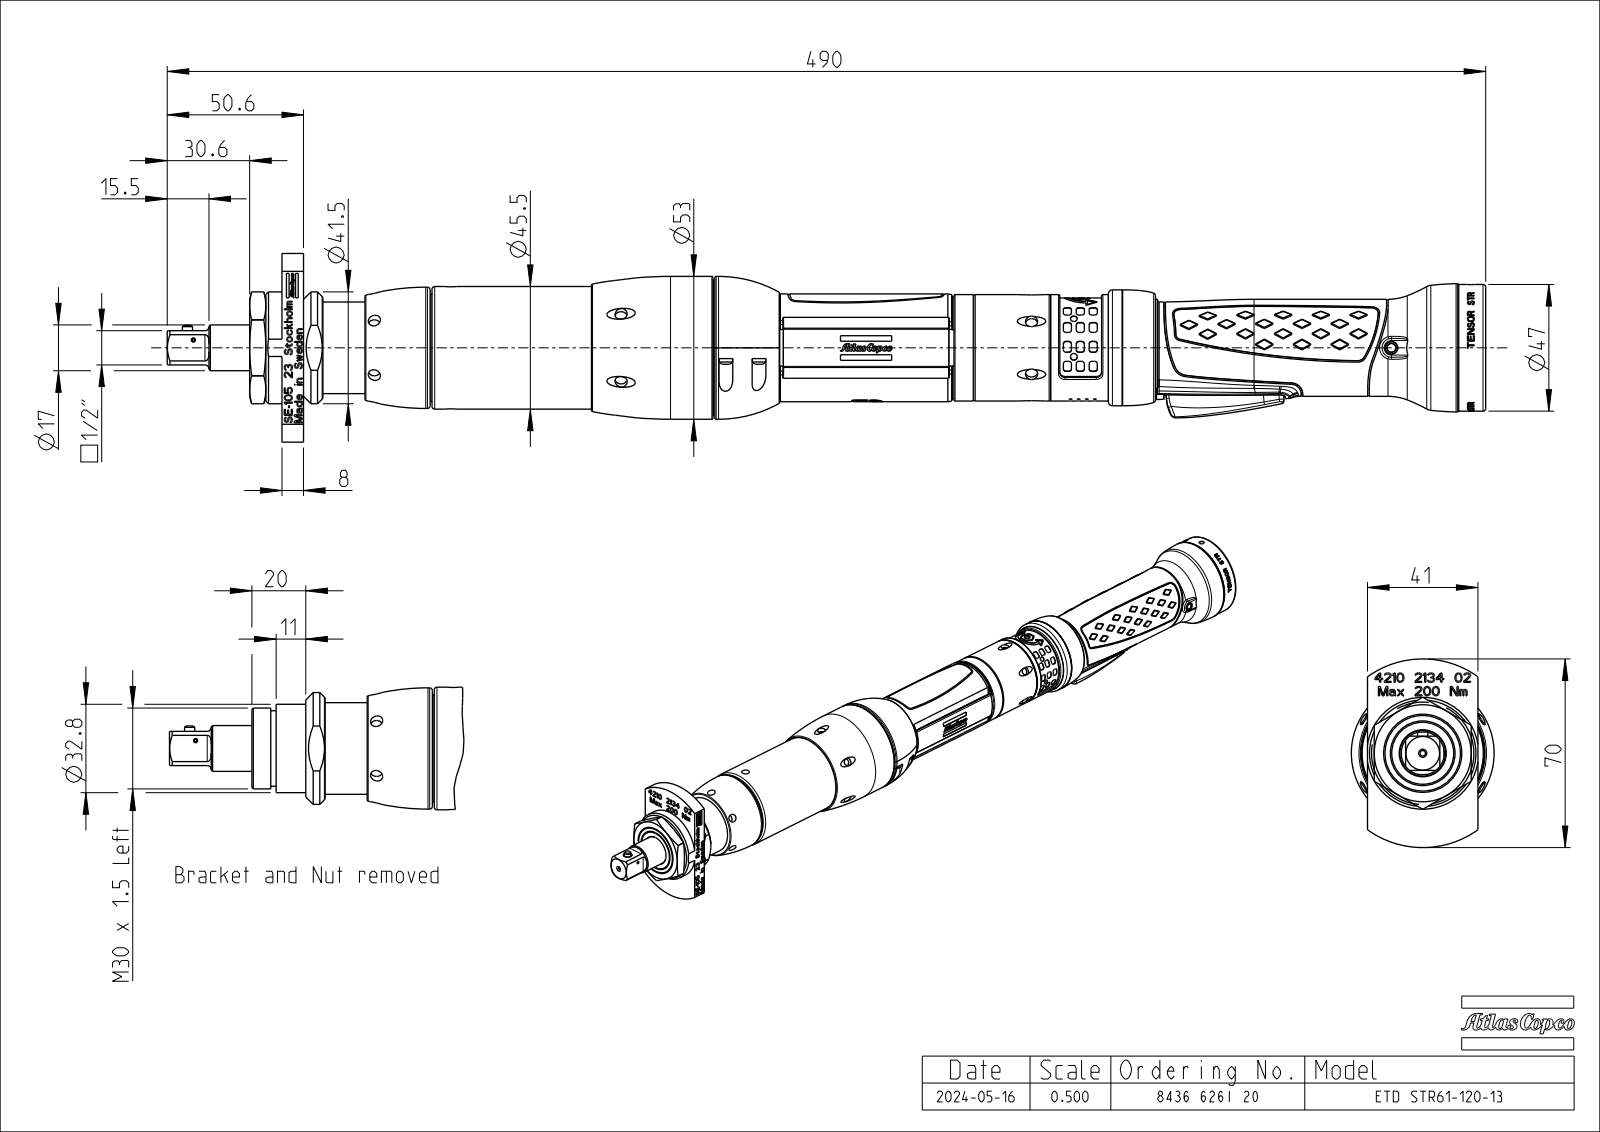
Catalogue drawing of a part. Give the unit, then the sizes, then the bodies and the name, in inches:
Units: inches
Overall size (bounding box): 19.271 × 2.756 × 2.087
Round holes (diameter × count): ⌀0.039 ×12, ⌀0.177 ×10, ⌀0.063 ×2, ⌀0.015 ×1, ⌀0.039 ×1, ⌀0.059 ×1, ⌀0.079 ×1, ⌀0.118 ×1, ⌀0.126 ×1, ⌀0.181 ×1, ⌀0.185 ×1, ⌀0.197 ×1
Round bosses / shafts (diameter × count): ⌀0.197 ×4, ⌀2.087 ×1, ⌀1.988 ×1, ⌀1.854 ×1, ⌀1.85 ×1, ⌀1.791 ×1, ⌀1.772 ×1, ⌀1.693 ×1
Partial cylindrical surfaces — rounded edges, fillets, slot ends (radius × count): R0.008 ×58, R0.012 ×44, R0.02 ×39, R0.009 ×24, R0.016 ×24, R0.079 ×14, R0.118 ×12, R0.024 ×4
Main face-to-face distances: 0.02, 0.075, 5.984, 5.909, 11.369, 11.294, 17.279, 6.224, 0.315, 17.594
Hole centre spacings: 0.118, 0.236, 0.354, 3.606, 5.999, 9.606, 0.196, 0.2
Volume: 39.83 in³ · Surface area: 145.3 in²
Bodies: 3 solids, 4276 faces (1817 planar, 713 cylindrical, 1746 other)
Part name (STEP PRODUCT): E1; E2; ASM0083_ASM
STEP written by: CREO PARAMETRIC BY PTC INC, 2022414 (AP242_MANAGED_MODEL_BASED_3D_ENGINEERING_MIM_LF)
